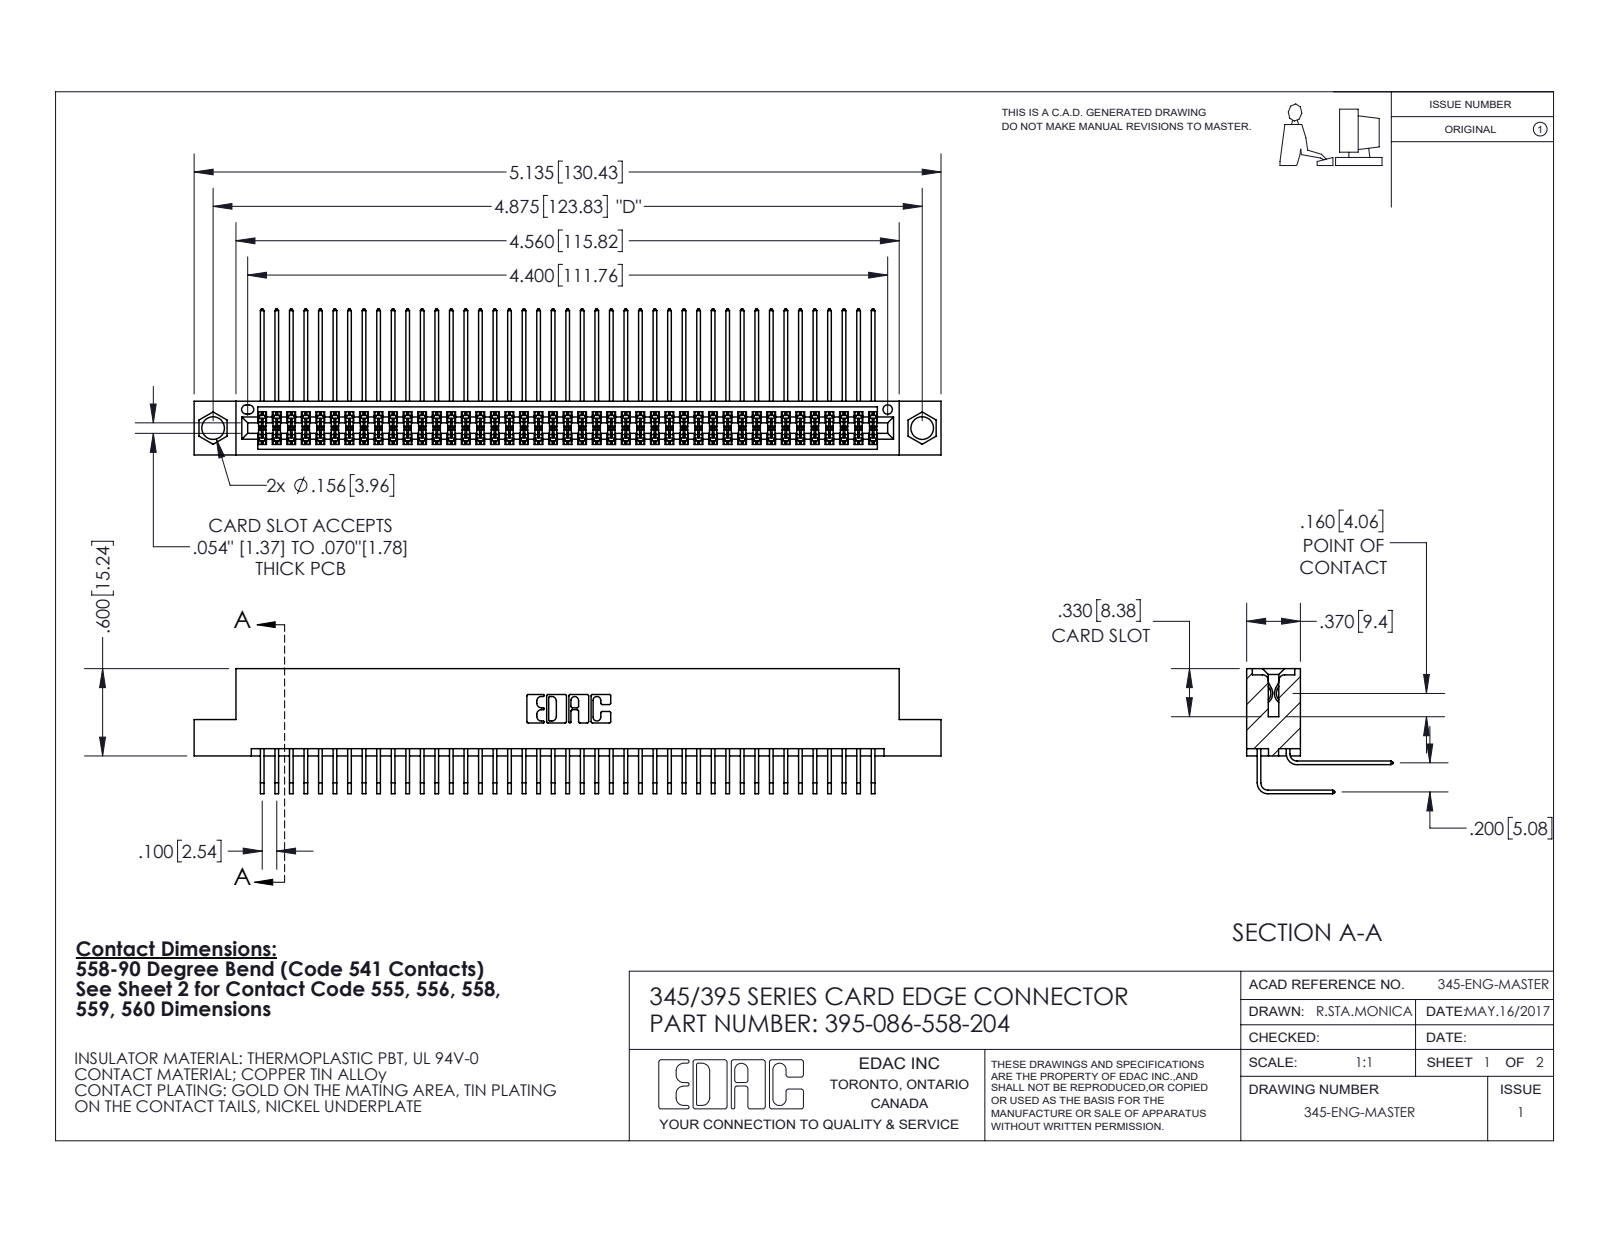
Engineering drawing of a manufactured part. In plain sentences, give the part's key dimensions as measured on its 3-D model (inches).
The part is named "345-292-001_558 559 Tail - 1; 345-292-001_558 Tail - 2; 395-086-558-204; 345 Part_Flush Mounting Lugs - 0.156 Dia-TI". Its 3-D file was written by "SolidWorks 2020 (CONFIG_CONTROL_DESIGN)". It is 87 solids with 4612 faces: 3104 planar, 1508 cylindrical and 0 other. Overall it measures 5.135 by 1.005 by 0.859 inches. Its volume is 0.798 cubic inches and its surface area 33.36 square inches. Round holes: 2 of diameter 0.156, 1 of diameter 0.064. Partial cylindrical surfaces (rounded edges, fillets, slot ends): 172 of radius 0.006, 22 of radius 0.01, 6 of radius 0.007, 6 of radius 0.031, 3 of radius 0.026, 2 of radius 0.014, 2 of radius 0.019, 2 of radius 0.022. The main face-to-face distances are 0.072, 0.298, 0.2, 0.37, 0.098, 0.272, 0.025, 0.225, 0.025, 0.175. The hole center spacings are 0.27, 4.639, 4.875.
